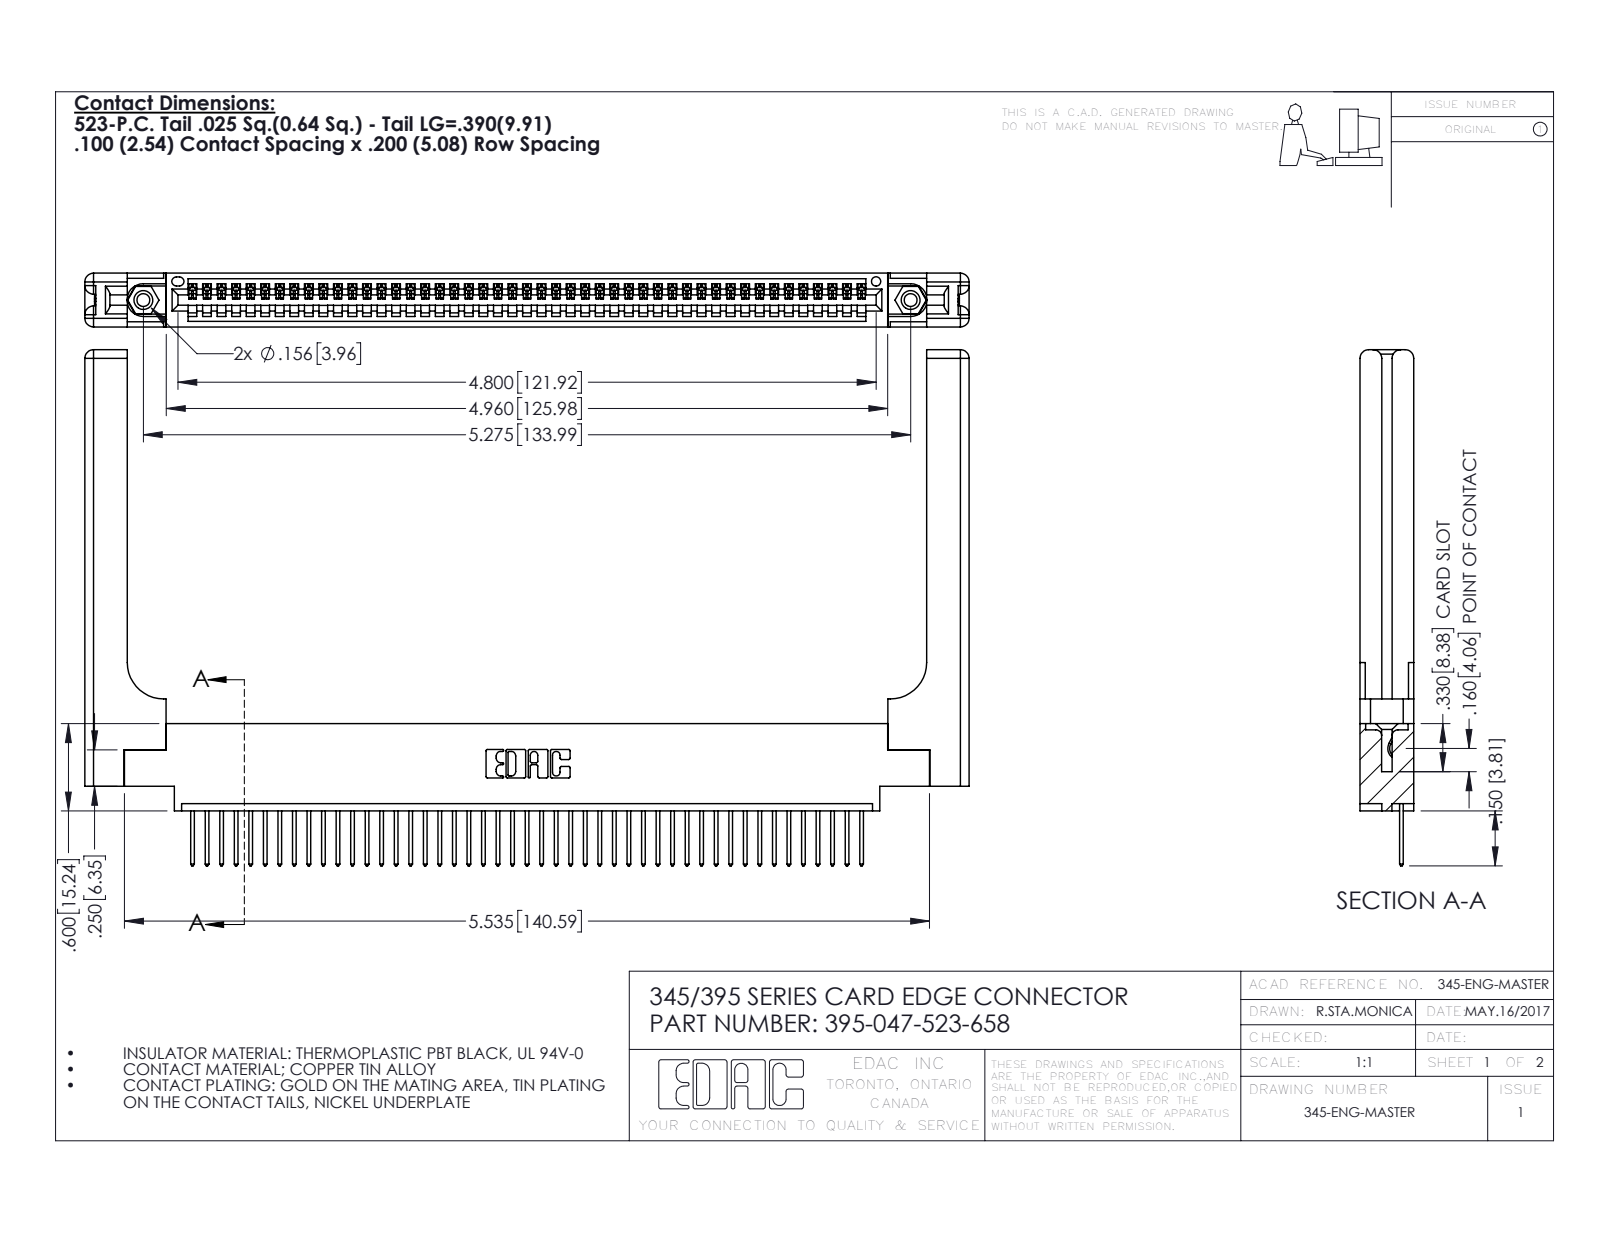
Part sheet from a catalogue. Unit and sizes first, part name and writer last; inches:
Units: inches
Overall size (bounding box): 6.079 × 3.547 × 0.37
Round holes (diameter × count): ⌀0.089 ×2, ⌀0.125 ×2, ⌀0.156 ×2, ⌀0.064 ×1
Round bosses / shafts (diameter × count): ⌀0.155 ×2
Partial cylindrical surfaces — rounded edges, fillets, slot ends (radius × count): R0.006 ×94, R0.01 ×94, R0.01 ×22, R0.06 ×16, R0.007 ×6, R0.031 ×6, R0.026 ×3, R0.03 ×2
Main face-to-face distances: 0.37, 0.072, 0.298, 0.098, 0.272, 0.025, 0.2, 0.225, 0.148, 0.15
Hole centre spacings: 0.27, 5.039, 5.275
Volume: 1.408 in³ · Surface area: 38.63 in²
Bodies: 52 solids, 3112 faces (2112 planar, 940 cylindrical, 60 other)
Part name (STEP PRODUCT): 345-250-001_345-250-001-102; 345 Part_0.170 Offset - 0.156 Dia-TH; 345-292-001_345-293-123; 395-047-523-658 (+1 more)
STEP written by: SolidWorks 2016 (CONFIG_CONTROL_DESIGN)
